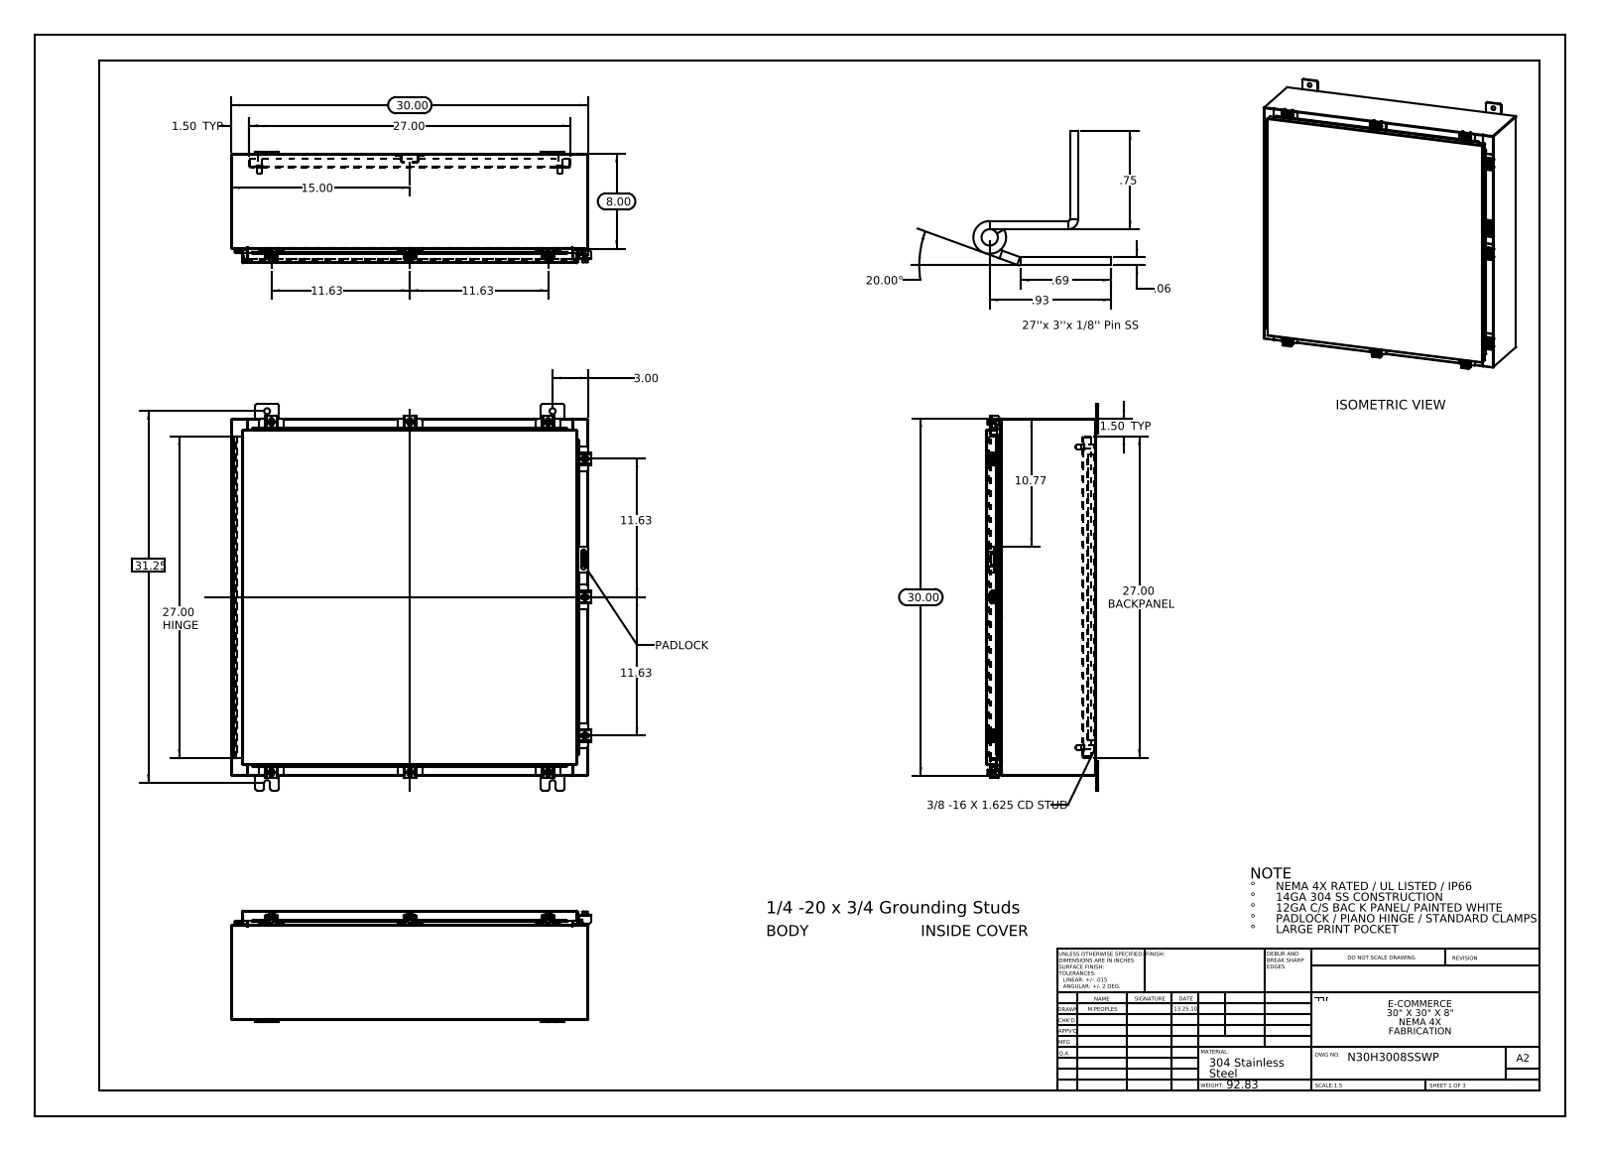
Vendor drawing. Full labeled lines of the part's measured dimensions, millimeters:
Part name (STEP PRODUCT): N30H3008SSWP Enclosure Stiffener; N30H3008SSWP Clamp Assembly; N30H3008SSWP Bottom; N30H3008SSWP Hinge Cover Side (+8 more)
STEP written by: SolidWorks 2013 (CONFIG_CONTROL_DESIGN)
Units: millimetres
Bodies: 63 solids, 2262 faces (1206 planar, 936 cylindrical, 120 other)
Overall size (bounding box): 825.5 × 767.4 × 238.5
Volume: 5 341 000 mm³ · Surface area: 5 245 000 mm²
Round holes (diameter × count): ⌀5.4 ×9, ⌀6.6 ×9, ⌀12.7 ×8, ⌀3.2 ×2, ⌀3.2 ×1
Round bosses / shafts (diameter × count): ⌀6.4 ×10, ⌀12.7 ×9, ⌀10.1 ×9, ⌀15.9 ×4, ⌀9.5 ×4, ⌀8.4 ×4
Partial cylindrical surfaces — rounded edges, fillets, slot ends (radius × count): R1.5 ×42, R0.3 ×31, R2.2 ×25, R4.8 ×24, R3 ×18, R3.6 ×18, R1.3 ×13, R2 ×12
Main face-to-face distances: 1.9, 231.8, 760.1, 229.9, 233.7, 2.6, 25.4, 206.4, 27.3, 204.5
Hole centre spacings: 59.1, 295.3, 325.1, 382.2, 695.2, 765.1, 804.2, 928.4
